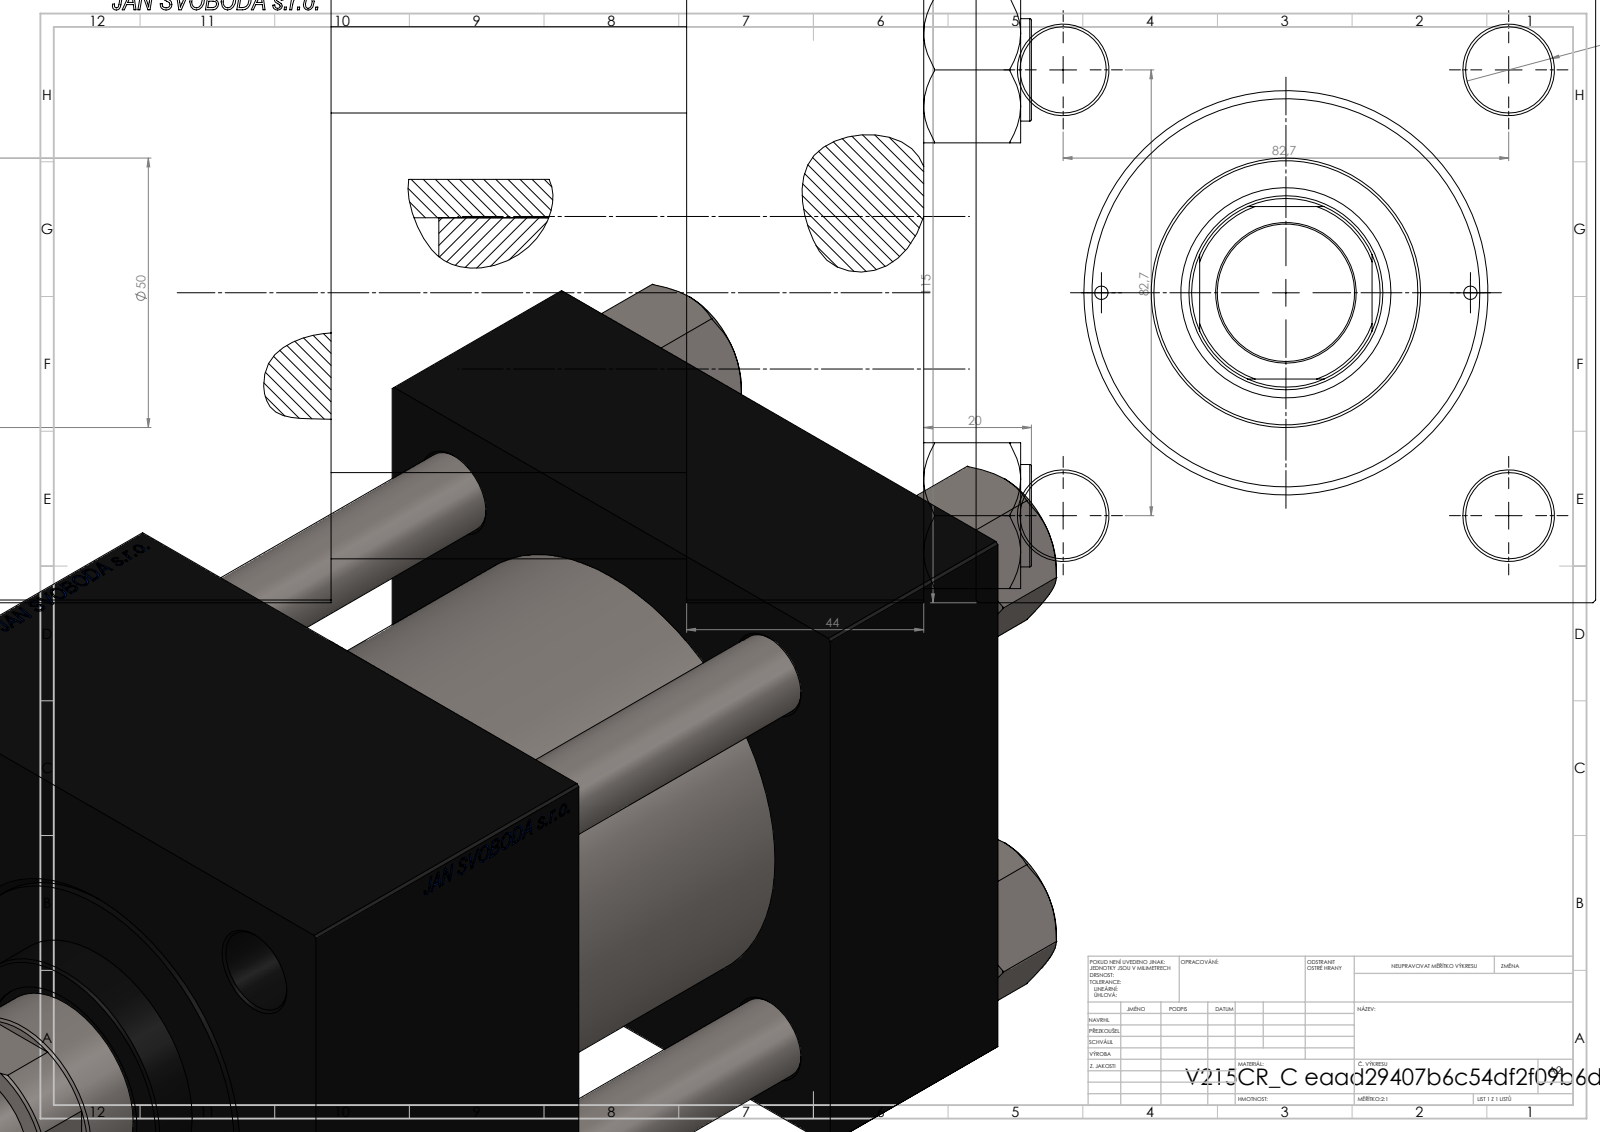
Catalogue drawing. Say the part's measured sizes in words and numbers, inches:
The part is named "NUT_M5_C; V215CR_C_TYCINKA; V215CR_VCP_C; V215CR_C_Body (+1 more)". Its 3-D file was written by "SolidWorks 2019 (CONFIG_CONTROL_DESIGN)". It is 11 solids with 1202 faces: 576 planar, 90 cylindrical and 536 other. Overall it measures 9.055 by 4.528 by 4.528 inches. Its volume is 109 cubic inches and its surface area 416.2 square inches. Round holes: 4 of diameter 0.63, 2 of diameter 0.098, 2 of diameter 0.276, 2 of diameter 1.041, 2 of diameter 1.378, 1 of diameter 1.004, 1 of diameter 1.417, 1 of diameter 1.535, 1 of diameter 2.402, 1 of diameter 2.835, 1 of diameter 3.15. Round bosses or shafts: 4 of diameter 0.748, 1 of diameter 3.386, 1 of diameter 1.969. Partial cylindrical surfaces (rounded edges, fillets, slot ends): 1 of radius 0.689. The main face-to-face distances are 4.528, 1.732, 7.047, 5.315, 4.331, 2.598, 2.717, 0.787, 5.917, 4.185. The hole center spacings are 1.652, 2.302, 3.256, 3.393, 1.348, 4.605, 2.697, 4.37.
